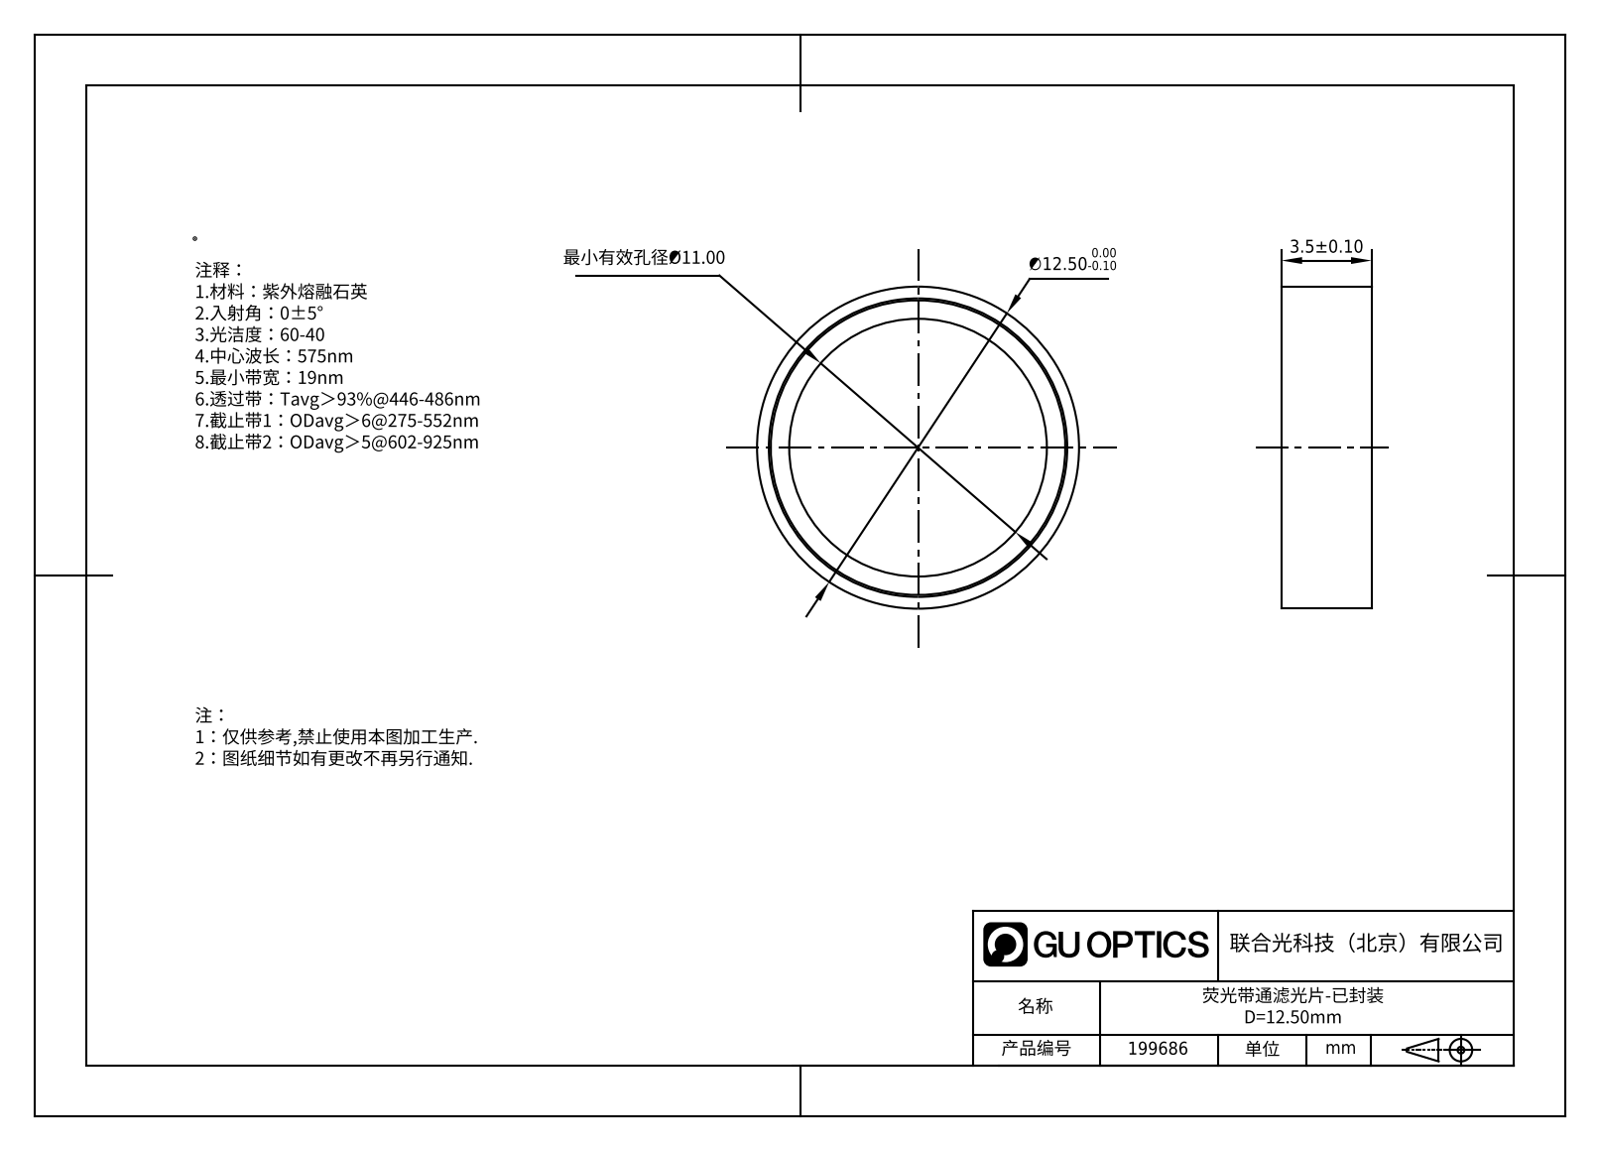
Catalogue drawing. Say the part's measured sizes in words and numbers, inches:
The part is named "199686". Its 3-D file was written by "SolidWorks 2019 (CONFIG_CONTROL_DESIGN)". It is 1 solid with 4 faces: 2 planar, 2 cylindrical and 0 other. Overall it measures 0.492 by 0.492 by 0.041 inches. Its volume is 0.008 cubic inches and its surface area 0.445 square inches. Round bosses or shafts: 1 of diameter 0.492. The main face-to-face distances are 0.041.
